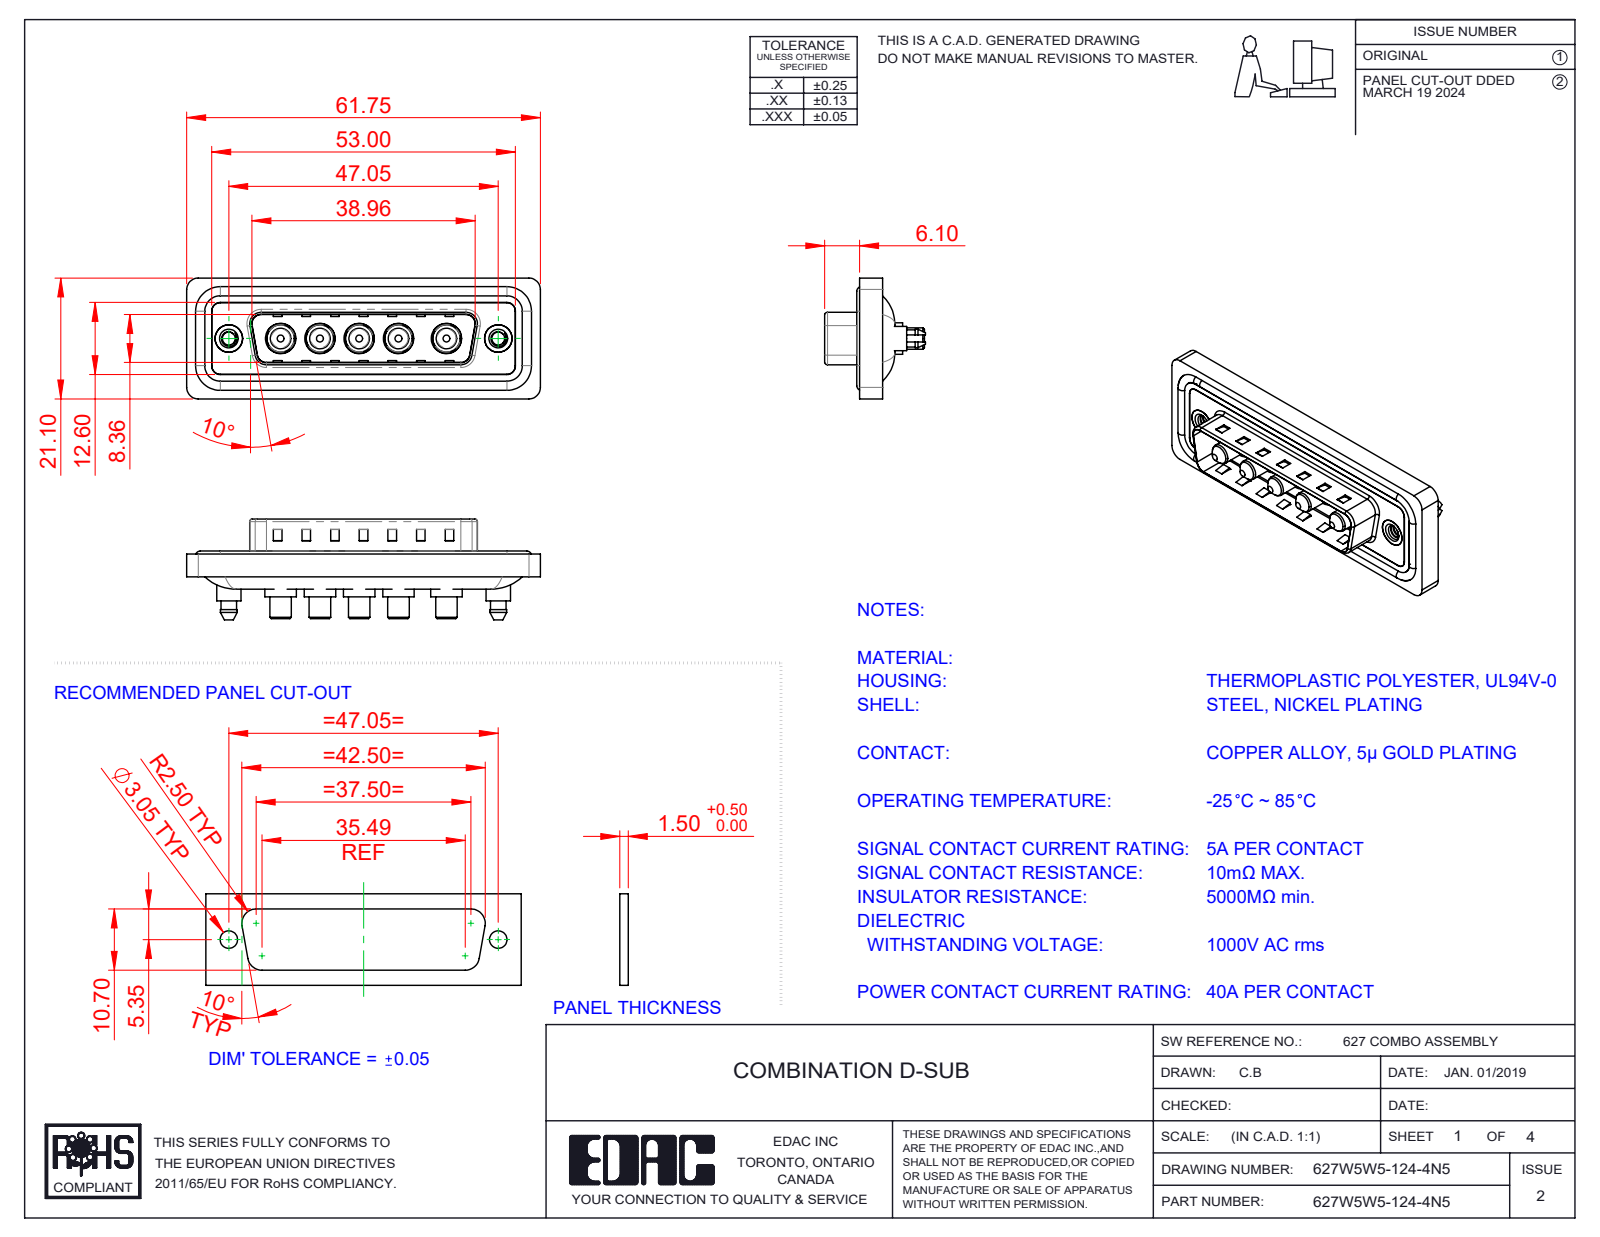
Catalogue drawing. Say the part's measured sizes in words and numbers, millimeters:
The part is named "627Combo Waterproof Housing_25 Contacts; 627Combo Shell Rear_25 Contacts; 627W5W5-124-4N5; Power Pin_40A S (+3 more)". Its 3-D file was written by "SolidWorks 2023 (CONFIG_CONTROL_DESIGN)". It is 17 solids with 728 faces: 275 planar, 315 cylindrical and 138 other. Overall it measures 61.75 by 21.1 by 17.6 millimeters. Its volume is 7 699 cubic millimeters and its surface area 12 184 square millimeters. Round holes: 5 of diameter 4.85, 5 of diameter 5.3, 2 of diameter 2.26, 2 of diameter 4, 2 of diameter 4.8, 2 of diameter 5. Round bosses or shafts: 5 of diameter 5.5, 5 of diameter 5.2, 5 of diameter 4.75, 5 of diameter 3.75, 5 of diameter 3.6, 4 of diameter 1.6, 2 of diameter 5.4, 2 of diameter 4.9. Partial cylindrical surfaces (rounded edges, fillets, slot ends): 24 of radius 1.5, 18 of radius 2, 10 of radius 1.6, 8 of radius 0.5, 5 of radius 2.1, 4 of radius 0.25, 4 of radius 0.6, 4 of radius 0.65. The main face-to-face distances are 0.4, 1.5, 3.1, 1.1, 0.5, 1.6, 2.9, 0.82, 9.58, 5.65. The hole center spacings are 6.86, 9.04, 13.73, 38.01, 6.87, 8.37, 8.38, 9.05.
